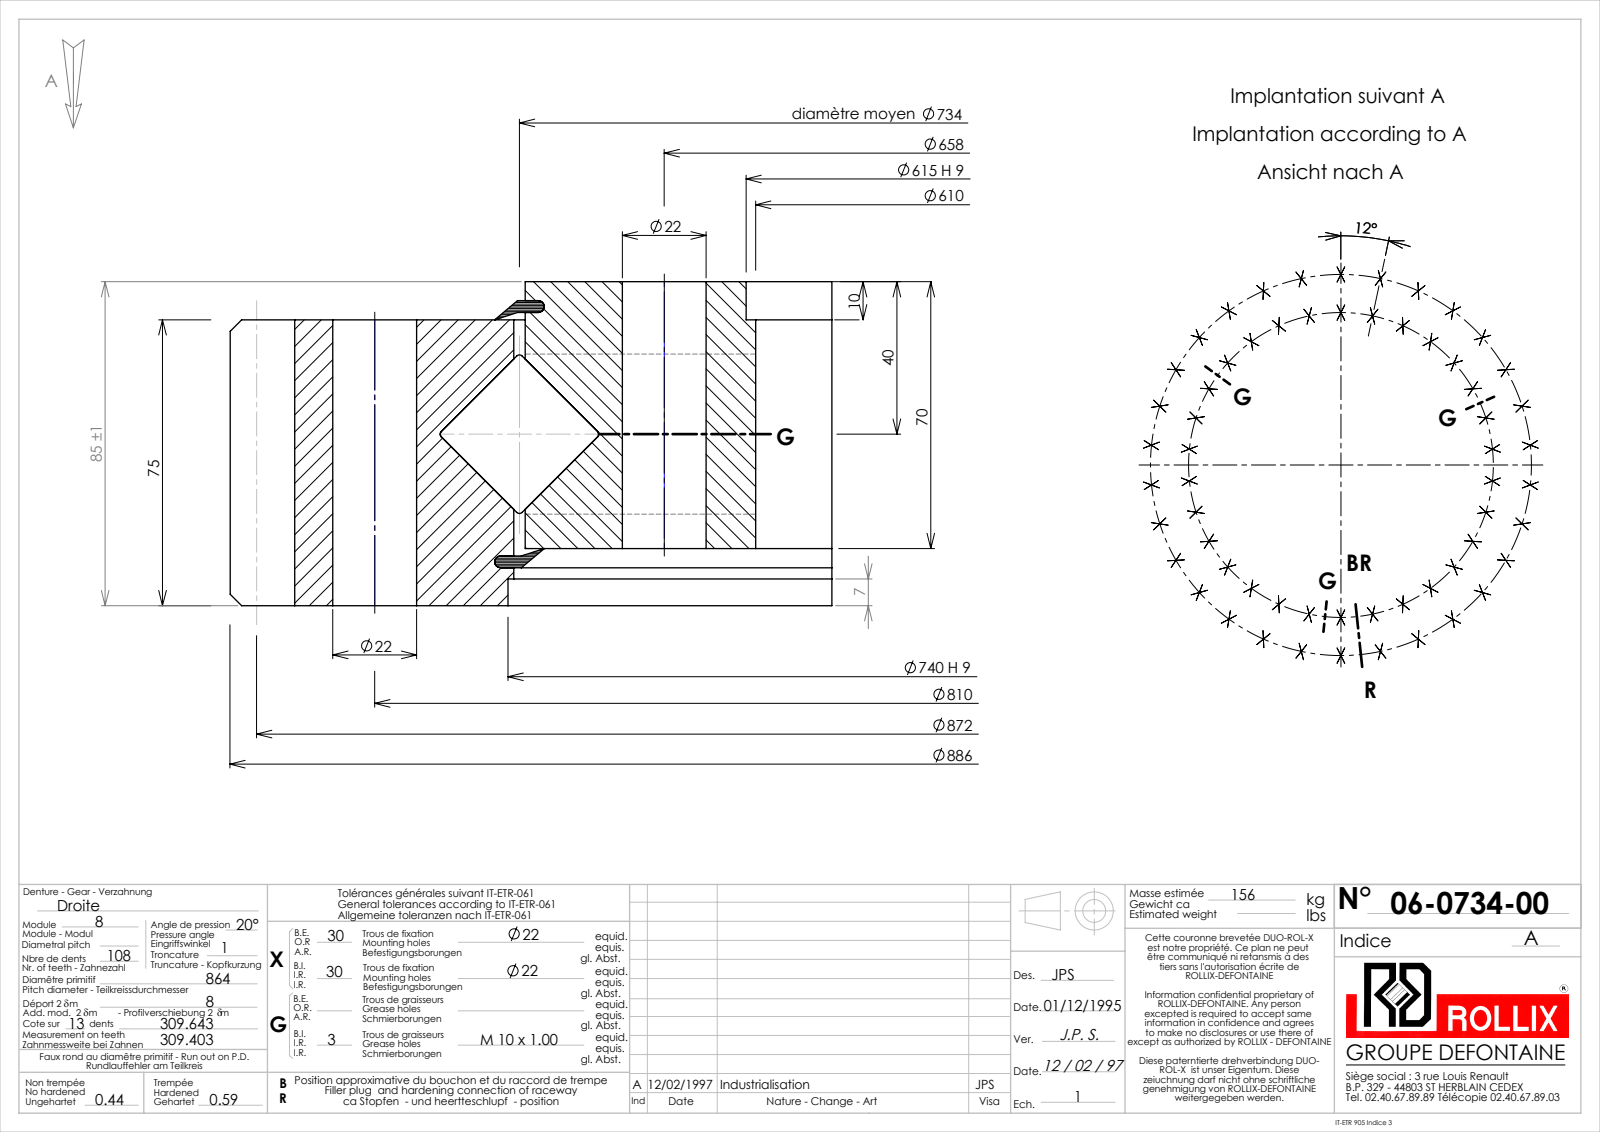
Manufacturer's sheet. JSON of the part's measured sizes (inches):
{"part_name": "06-0734-00", "step_written_by": "SolidWorks 2016 (CONFIG_CONTROL_DESIGN)", "units": "inches", "bodies": {"solids": 5, "faces": 853, "planar": 232, "cylindrical": 363, "other": 258}, "overall_size": [34.875, 34.875, 3.346], "volume_in3": 1106, "surface_area_in2": 3055, "round_holes": [[0.866, 60], [0.354, 3], [24.016, 1], [24.213, 1], [29.016, 1], [29.134, 1]], "round_bosses_or_shafts": [[28.78, 1], [1.181, 1]], "partial_cylinders_radius": [[16.772, 1], [17.441, 1]], "face_to_face_distances": [2.953, 0.591, 2.362, 3.346, 2.756, 0.394, 0.199, 2.561, 0.077, 2.439], "hole_center_spacings": [27.617, 31.193, 31.715, 6.63, 29.133, 12.971, 15.945, 3.333]}
